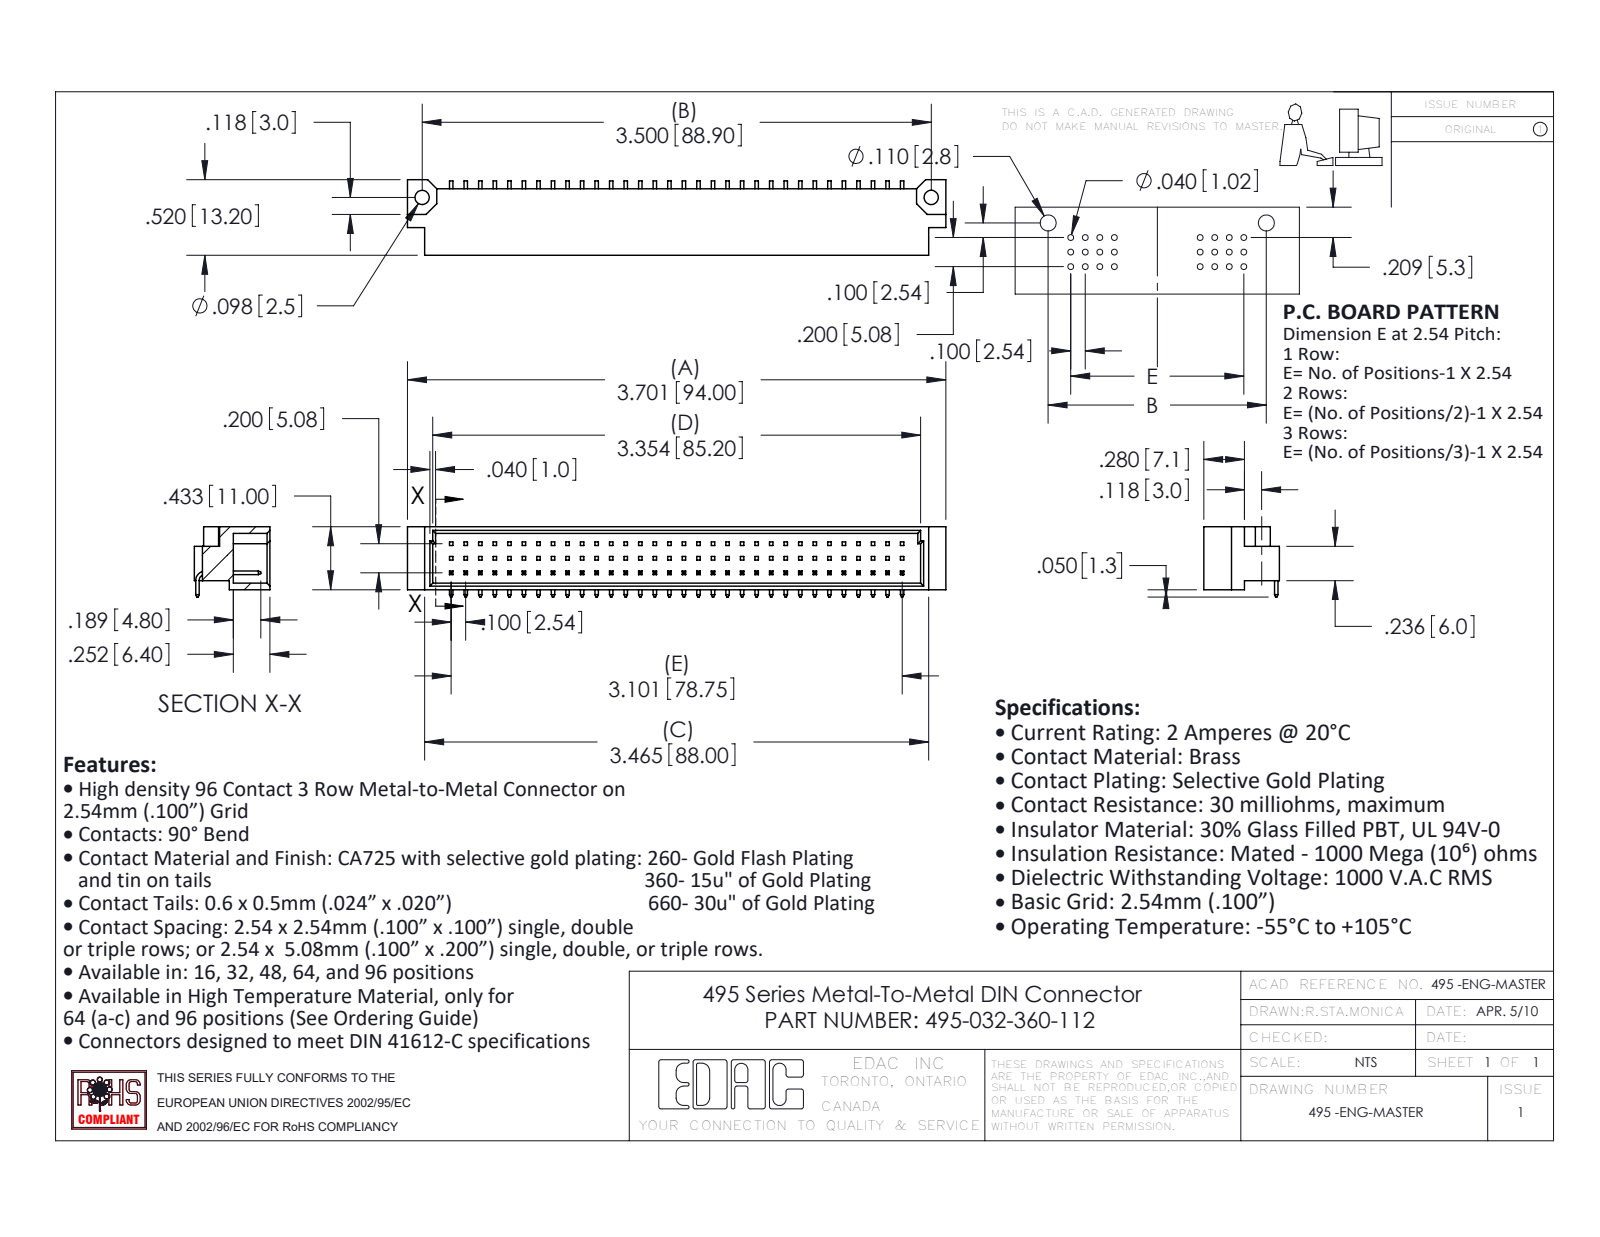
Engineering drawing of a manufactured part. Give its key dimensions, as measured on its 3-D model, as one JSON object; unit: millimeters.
{"part_name": "495-032-360-112; 495 Part_96; 495-290-3", "step_written_by": "SolidWorks 2020 (AUTOMOTIVE_DESIGN)", "units": "millimeters", "bodies": {"solids": 33, "faces": 1009, "planar": 941, "cylindrical": 68, "other": 0}, "overall_size": [94, 13.2, 12.27], "volume_mm3": 6100, "surface_area_mm2": 7981, "round_holes": [[2.49, 2]], "partial_cylinders_radius": [[1.02, 1], [1.65, 1]], "face_to_face_distances": [1.14, 9.86, 5.2, 11, 2.54, 0.61, 8.72, 1.6, 9.4, 0.46], "hole_center_spacings": [88.9]}
